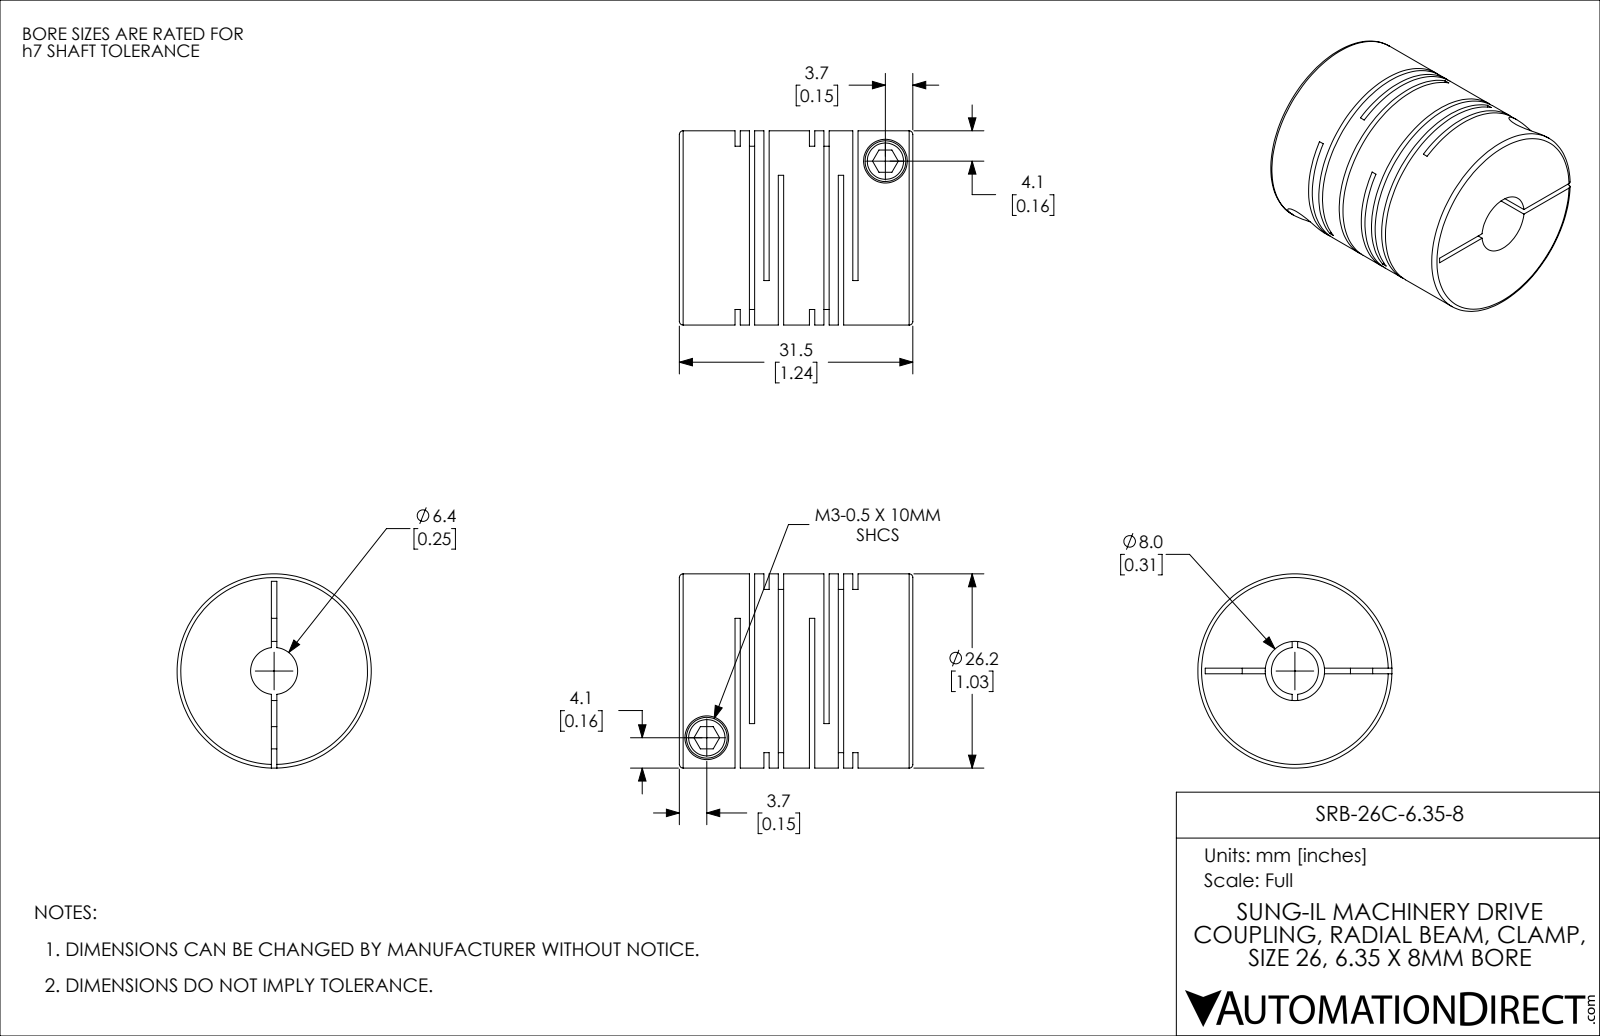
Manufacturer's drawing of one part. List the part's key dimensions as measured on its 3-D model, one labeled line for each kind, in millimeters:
Part name (STEP PRODUCT): SRB-26C-6.35-8
STEP written by: SolidWorks 2021 (CONFIG_CONTROL_DESIGN)
Units: millimetres
Bodies: 1 solid, 114 faces (60 planar, 42 cylindrical, 12 other)
Overall size (bounding box): 31.5 × 26.2 × 26.2
Volume: 12 781 mm³ · Surface area: 11 146 mm²
Round holes (diameter × count): ⌀3 ×2, ⌀5.9 ×2, ⌀6.35 ×1, ⌀8 ×1
Round bosses / shafts (diameter × count): ⌀5.5 ×2, ⌀26.2 ×1
Main face-to-face distances: 1.95, 10.05, 0.71, 3.9, 8.1, 12, 1.24, 2.66, 9.34, 13.95
